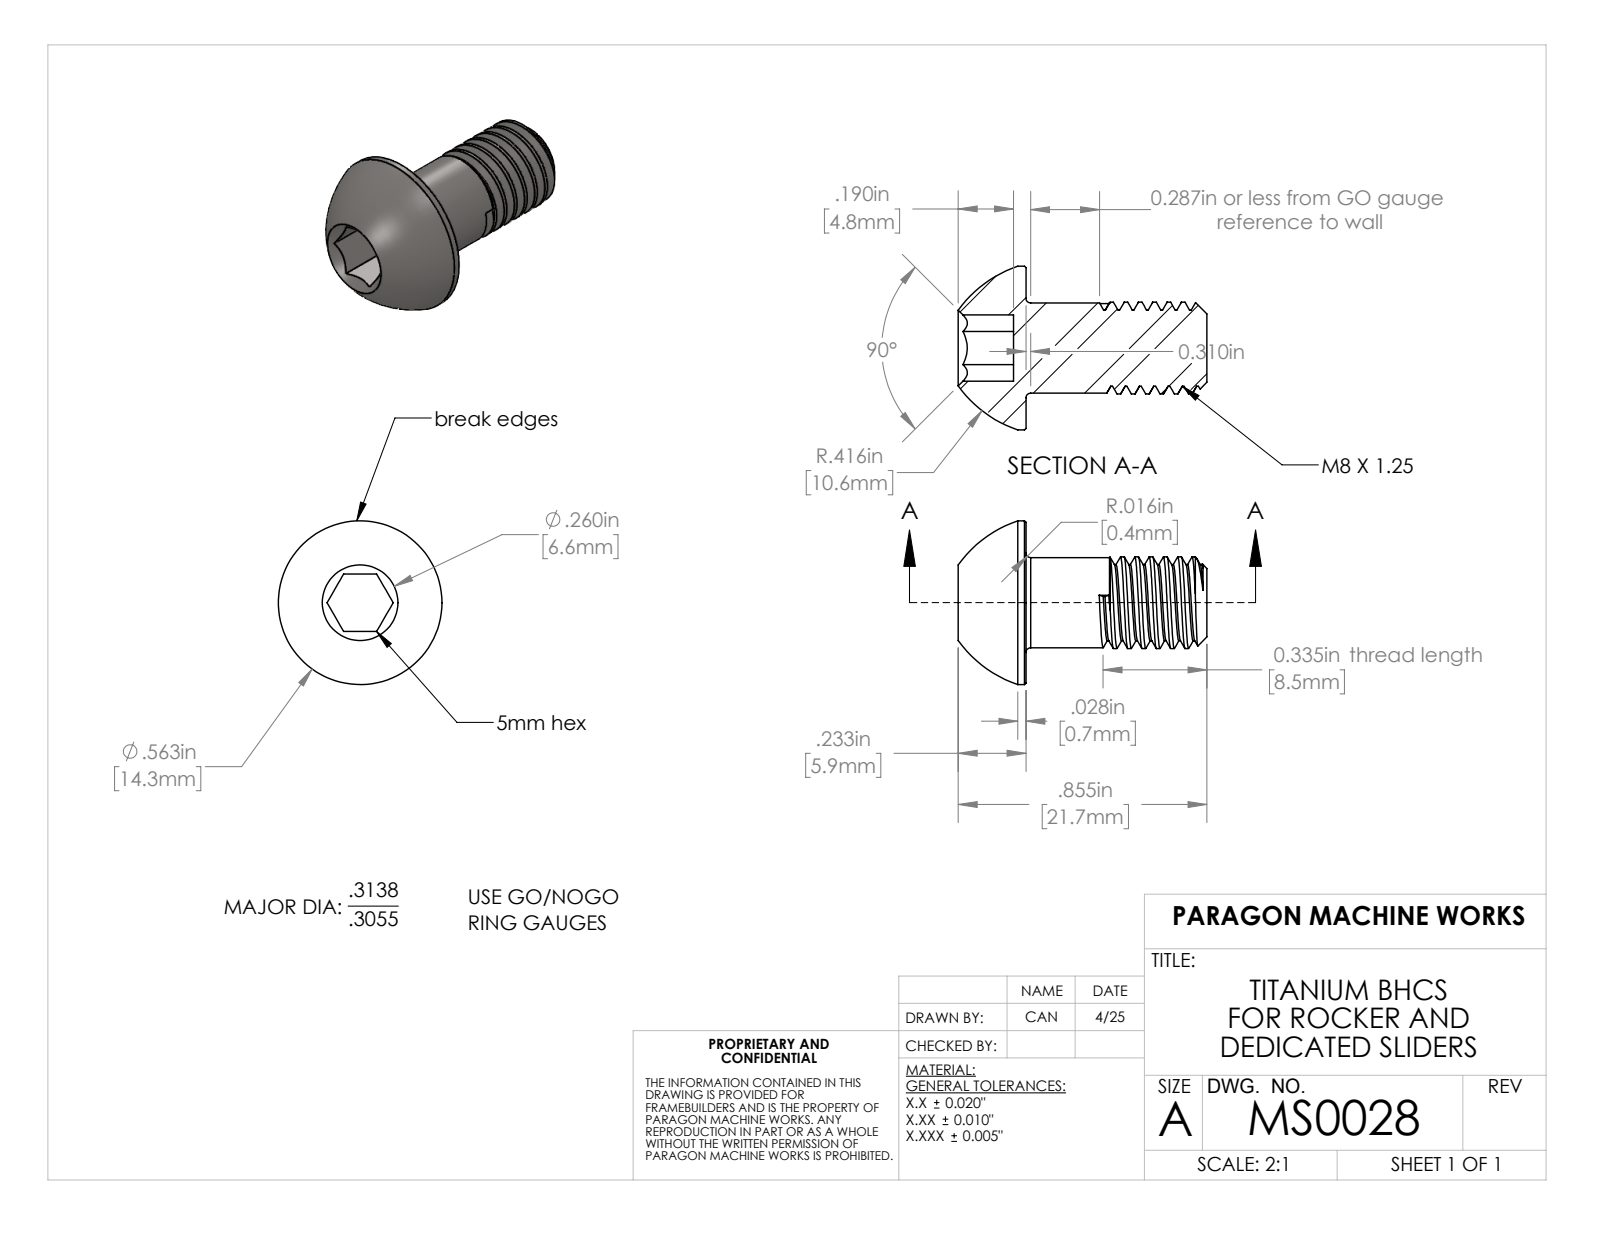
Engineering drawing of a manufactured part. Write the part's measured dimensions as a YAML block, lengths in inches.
part_name: "MS0028"
step_written_by: "SolidWorks 2023 (AUTOMOTIVE_DESIGN)"
units: inches
bodies: {solids: 1, faces: 42, planar: 10, cylindrical: 18, other: 14}
overall_size: [0.855, 0.562, 0.562]
volume: 0.077
surface_area: 1.556
round_bosses_or_shafts:
  - {diameter: 0.563, count: 1}
  - {diameter: 0.315, count: 1}
  - {diameter: 0.31, count: 1}
face_to_face_distances: [0.197, 0.622, 0.043, 0.665]
